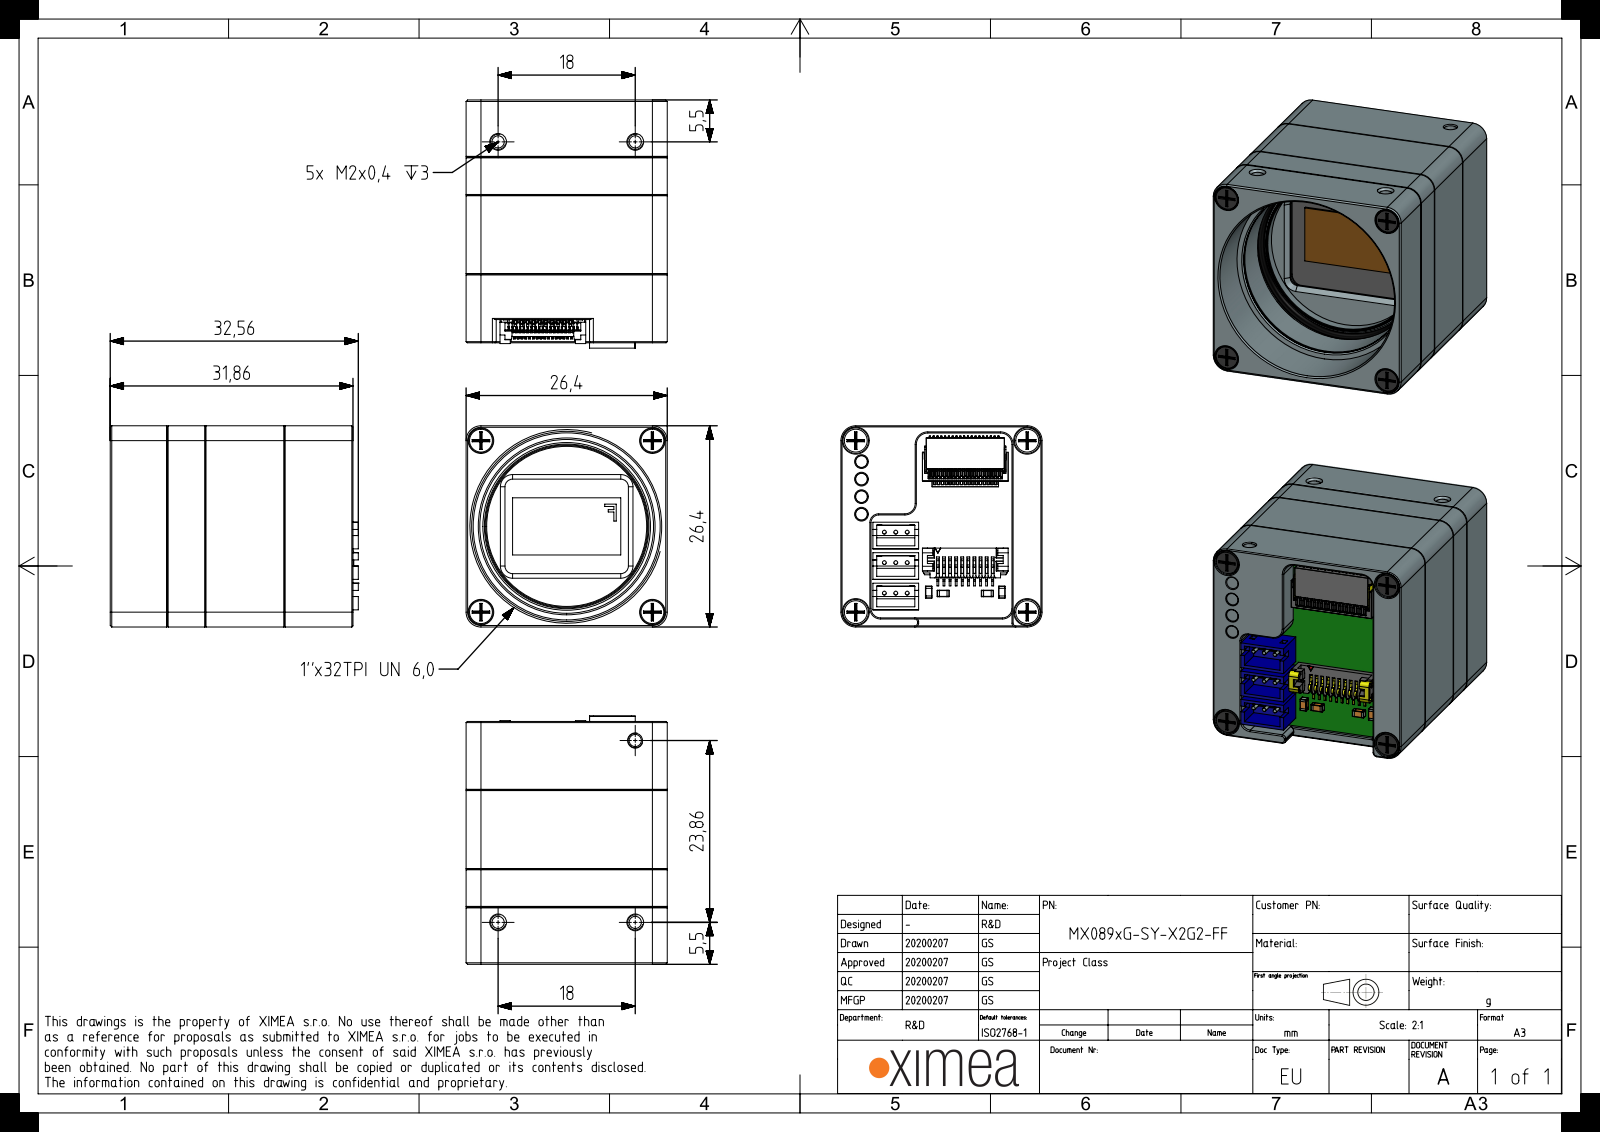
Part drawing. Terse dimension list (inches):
name: MX-X2G2-MAIN-FF-PCA-REV2; MECH-THERM-PAD-10X5X1; SROB-M2x4-CUST; MX-X2G2-CONN-FF-PCA (+8 more)
written by: SIEMENS PLM Software NX 1907 (AUTOMOTIVE_DESIGN)
unit: in
bodies: 306 solids, 20263 faces (11969 planar, 5735 cylindrical, 2559 other)
size: 1.282 × 1.039 × 1.039
volume: 0.698 in³; area: 36.12 in²
holes: 15× ⌀0.063, 9× ⌀0.028, 8× ⌀0.079, 4× ⌀0.035, 4× ⌀0.035, 4× ⌀0.083, 4× ⌀0.118, 4× ⌀0.126, 4× ⌀0.132, 3× ⌀0.012, 2× ⌀0.024, 2× ⌀0.03
bosses: 9× ⌀0.02, 8× ⌀0.075, 6× ⌀0.118, 4× ⌀0.064, 4× ⌀0.033, 2× ⌀0.063, 2× ⌀0.031, 1× ⌀0.984
rounds: 77× R0.004, 74× R0.005, 30× R0.006, 30× R0.013, 27× R0.015, 18× R0.039, 18× R0.059, 15× R0.008
face distances: 0.039, 0.142, 1.039, 0.181, 0.27, 0.451, 0.412, 0.1, 0.224, 0.165
hole spacings: 0.168, 0.515, 0.626, 0.059, 0.157, 0.886, 0.091, 0.139
